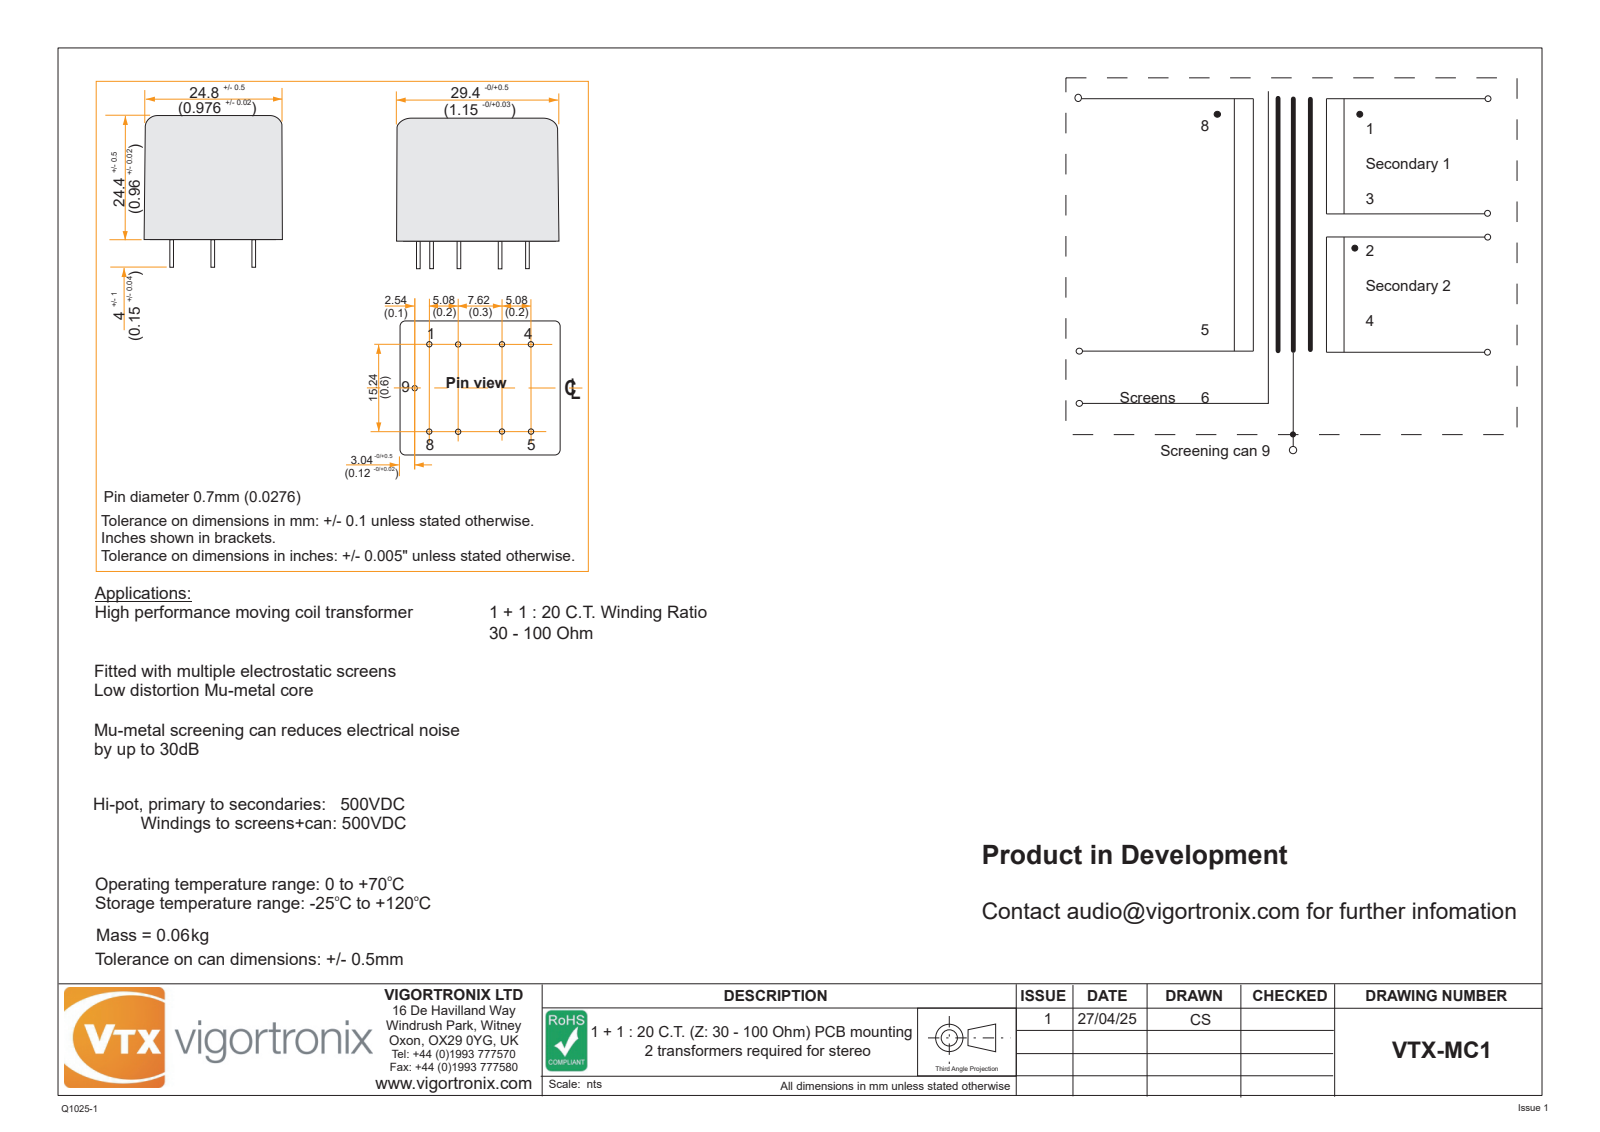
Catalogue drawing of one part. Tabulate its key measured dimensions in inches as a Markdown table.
| quantity | value |
| --- | --- |
| part name | VTX-MC1 BOBBIN; VTX-MC1; VTX-MC1 CAN; VTX-MC1 LID |
| STEP written by | SolidWorks 2024 (AUTOMOTIVE_DESIGN) |
| units | inches |
| bodies | 3 solids, 127 faces (35 planar, 72 cylindrical, 20 other) |
| overall size | 1.166 × 1.126 × 0.993 |
| volume | 0.934 in³ |
| surface area | 16.81 in² |
| round holes (diameter × count) | 0.138 × 8, 0.059 × 1 |
| round bosses / shafts (diameter × count) | 0.028 × 7 |
| partial cylindrical surfaces (radius × count) | 0.02 × 20, 0.075 × 8, 0.098 × 8, 0.079 × 4 |
| main face-to-face distances | 0.024, 0.921, 0.898, 0.886, 0.035, 0.909, 0.945, 0.906, 1.083, 0.102 |
| hole center spacings | 0.2, 0.5, 0.6, 0.632, 0.671, 0.781, 0.3, 0.316 |
